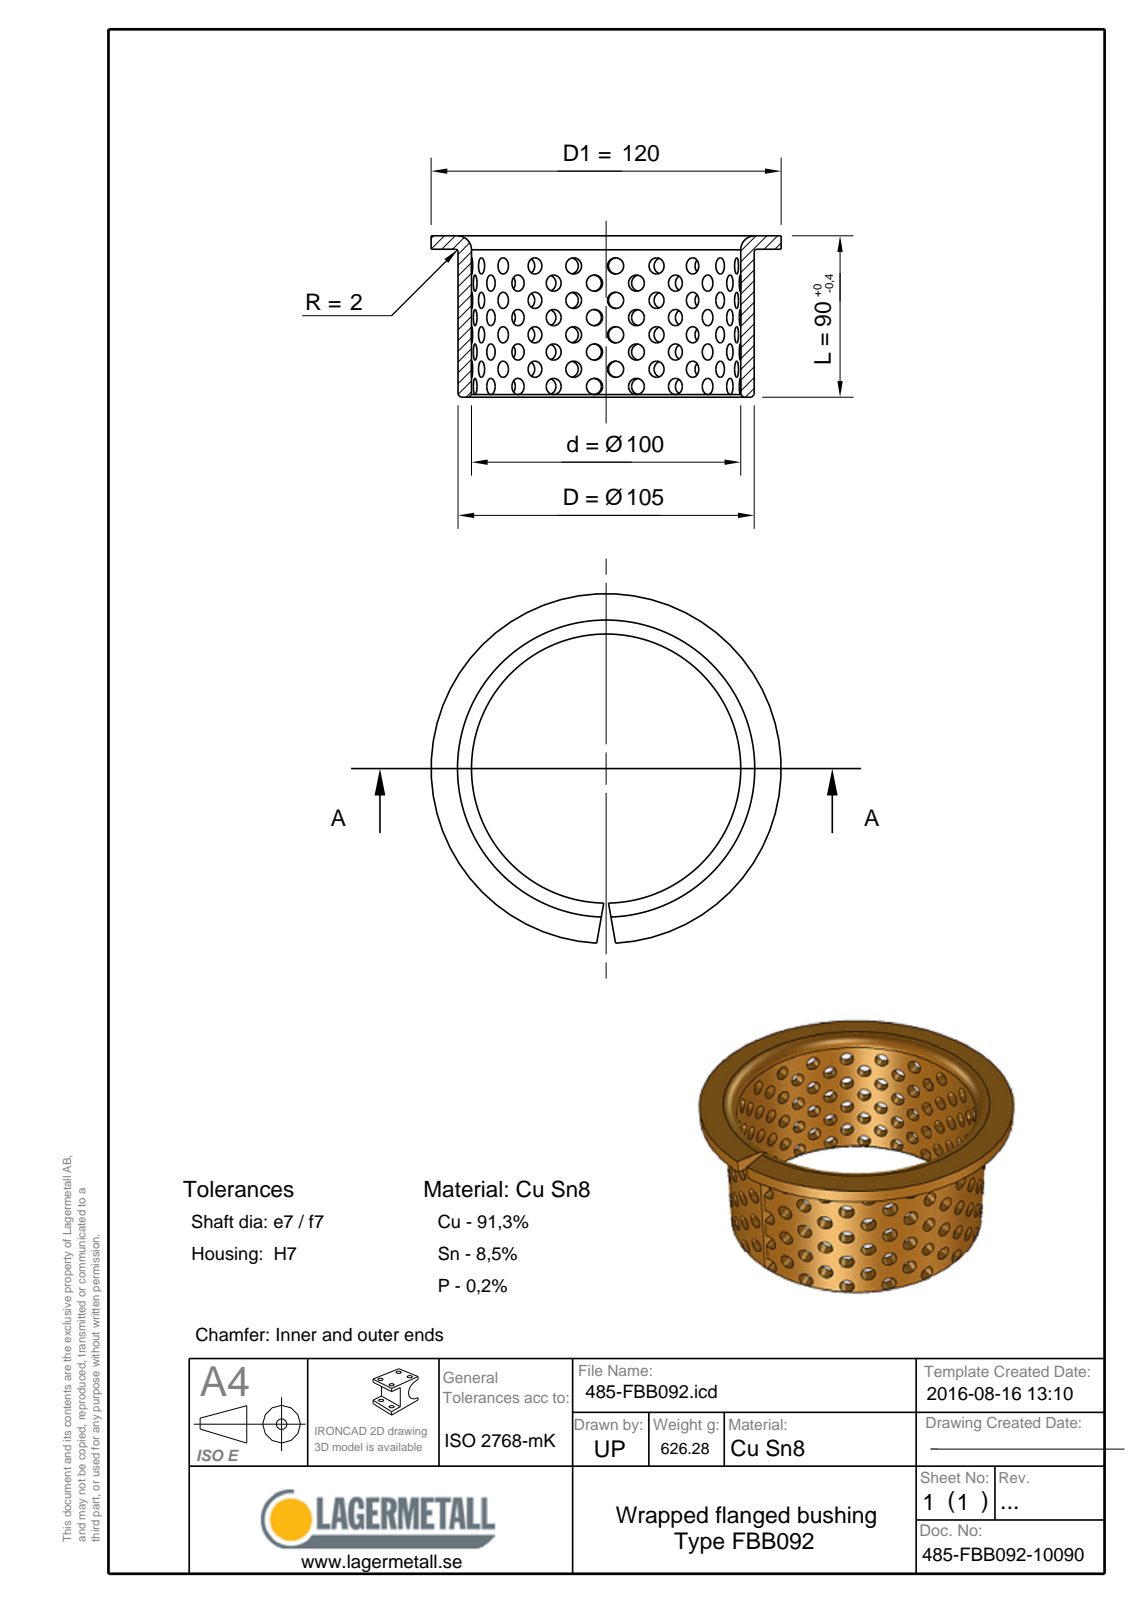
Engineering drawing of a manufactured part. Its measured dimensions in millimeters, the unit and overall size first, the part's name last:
Units: millimetres
Overall size (bounding box): 120 × 119.96 × 90
Round holes (diameter × count): ⌀100 ×1
Round bosses / shafts (diameter × count): ⌀120 ×1, ⌀105 ×1
Main face-to-face distances: 2.5, 87.5, 90
Volume: 77 318 mm³ · Surface area: 63 976 mm²
Bodies: 1 solid, 12 faces (5 planar, 3 cylindrical, 4 other)
Part name (STEP PRODUCT): 485-FBB092-10090
STEP written by: Spatial InterOp 3D (CONFIG_CONTROL_DESIGN)
